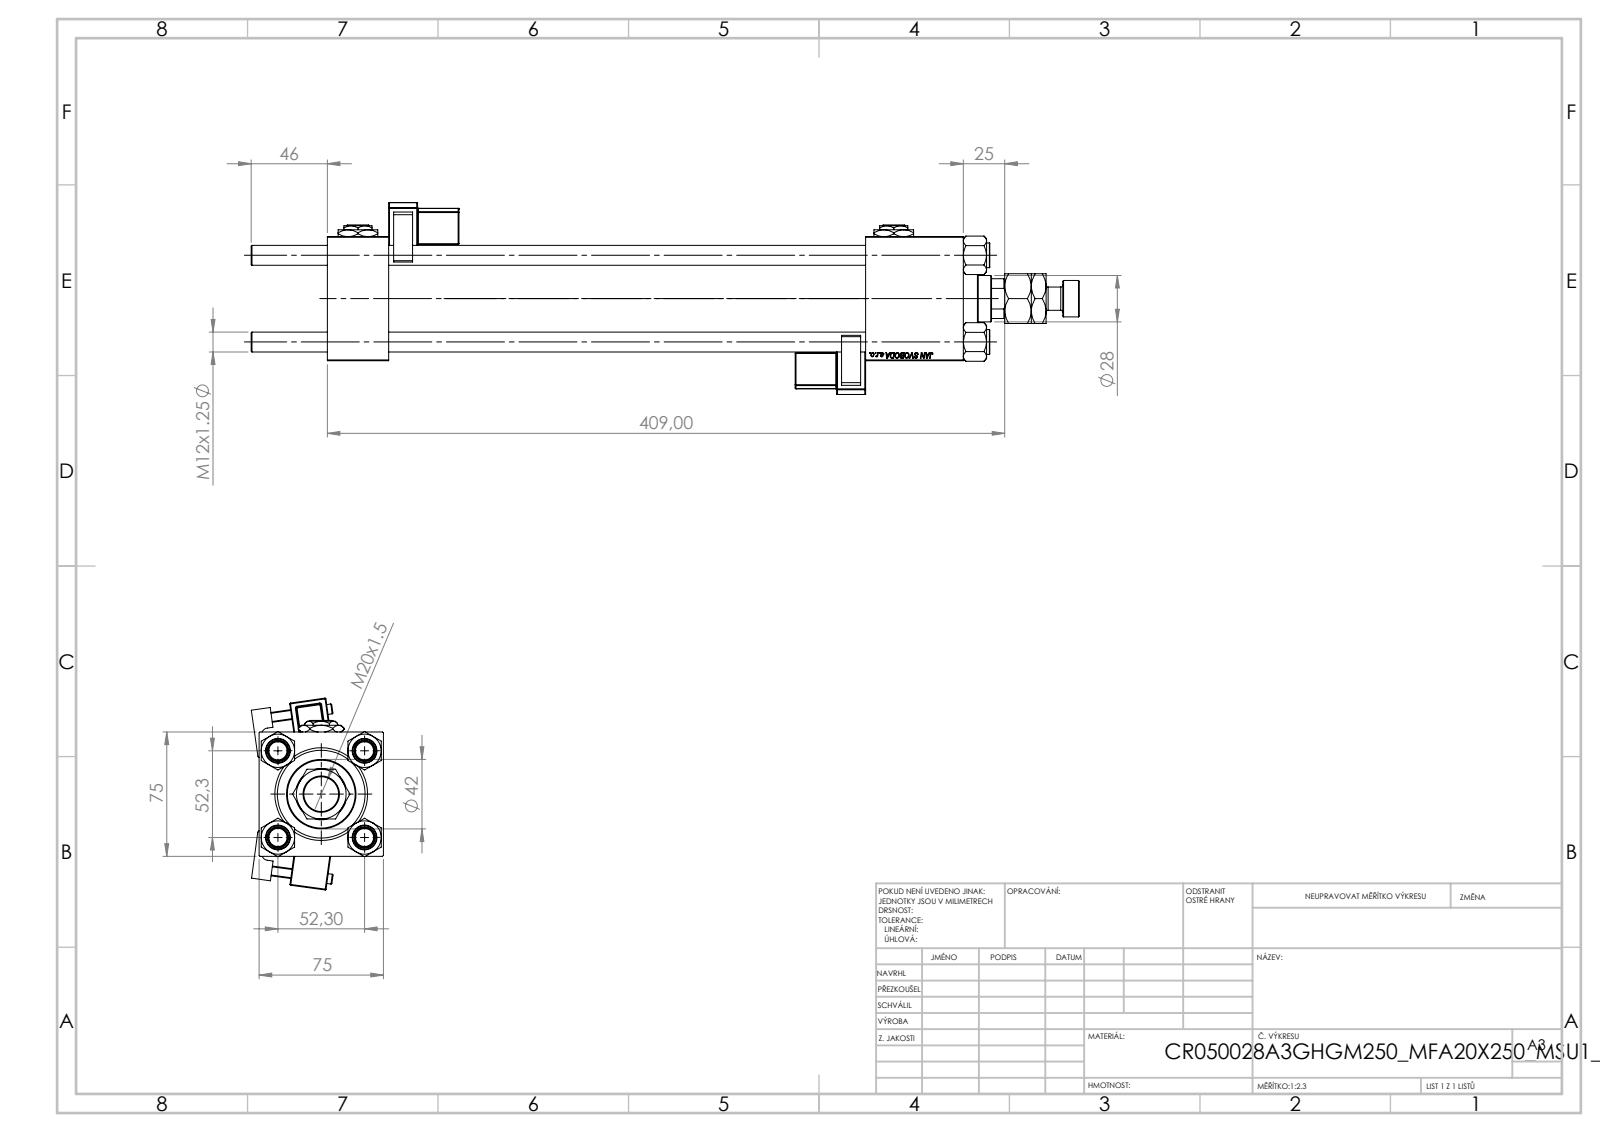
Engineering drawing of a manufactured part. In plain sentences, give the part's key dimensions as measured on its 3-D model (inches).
The part is named "MFA; V215CR_VCP; V215CR_BODY_A; V215CR_MSU (+4 more)". Its 3-D file was written by "SolidWorks 2019 (CONFIG_CONTROL_DESIGN)". It is 16 solids with 1439 faces: 641 planar, 152 cylindrical and 646 other. Overall it measures 19.685 by 4.557 by 3.137 inches. Its volume is 68.53 cubic inches and its surface area 497.9 square inches. Round holes: 4 of diameter 0.472, 2 of diameter 0.276, 2 of diameter 0.825, 2 of diameter 1.181, 1 of diameter 0.728, 1 of diameter 1.102, 1 of diameter 1.22, 1 of diameter 1.614, 1 of diameter 1.969, 1 of diameter 2.087. Round bosses or shafts: 4 of diameter 0.591, 2 of diameter 0.236, 1 of diameter 2.205, 1 of diameter 1.654, 1 of diameter 0.866, 1 of diameter 0.551. Partial cylindrical surfaces (rounded edges, fillets, slot ends): 48 of radius 0.02, 2 of radius 0.039, 2 of radius 0.098, 2 of radius 0.157, 1 of radius 0.531. The main face-to-face distances are 2.953, 1.457, 12.795, 15.118, 13.661, 2.323, 11.339, 13.988, 12.531, 1.193. The hole center spacings are 1.456, 2.059, 2.912, 12.736.
